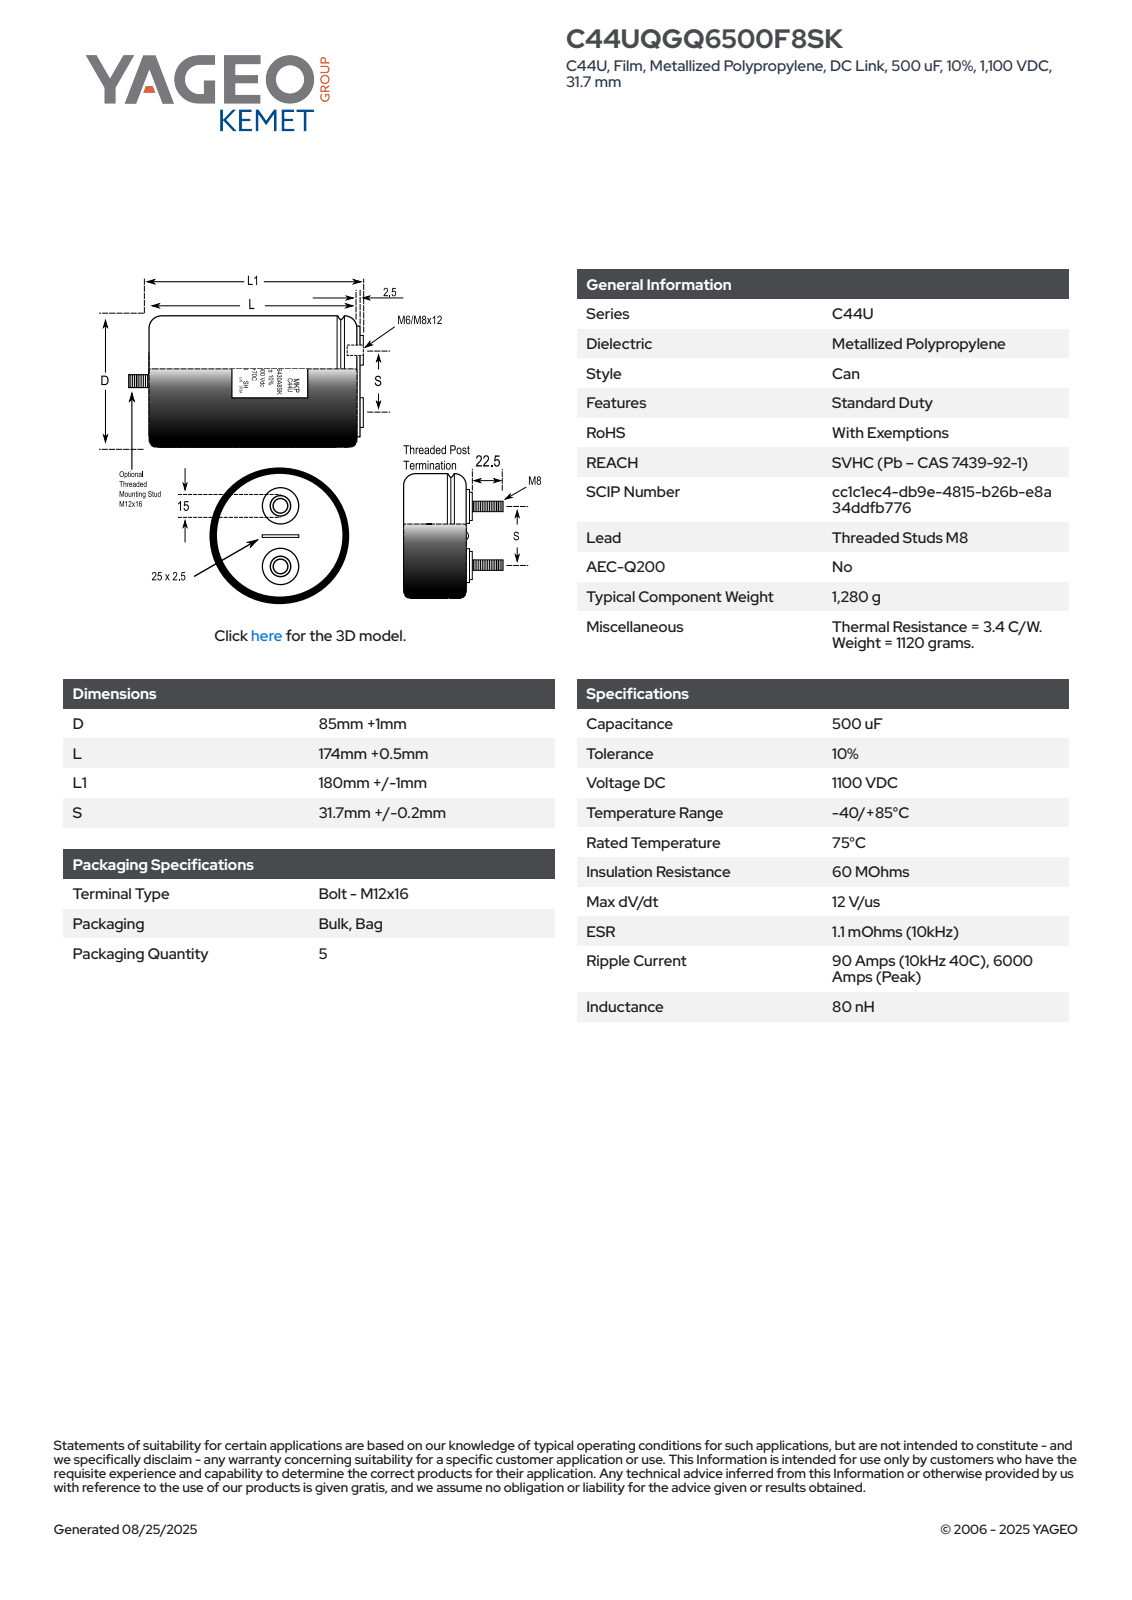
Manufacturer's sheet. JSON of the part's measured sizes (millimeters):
{"part_name": "CFP_C44U_Q_85X174_D86L174.5S31.9", "step_written_by": "SolidWorks 2021 (AUTOMOTIVE_DESIGN)", "units": "millimeters", "bodies": {"solids": 1, "faces": 104, "planar": 36, "cylindrical": 29, "other": 39}, "overall_size": [215.5, 86, 86], "volume_mm3": 1011000, "surface_area_mm2": 59178, "round_bosses_or_shafts": [[18, 2], [15, 2], [8, 2], [86, 1], [70, 1], [12, 1]], "partial_cylinders_radius": [[42.99, 1]], "face_to_face_distances": [174.5, 1.25, 2.5, 177, 175.75, 16, 190.5, 191.75, 193, 25]}
